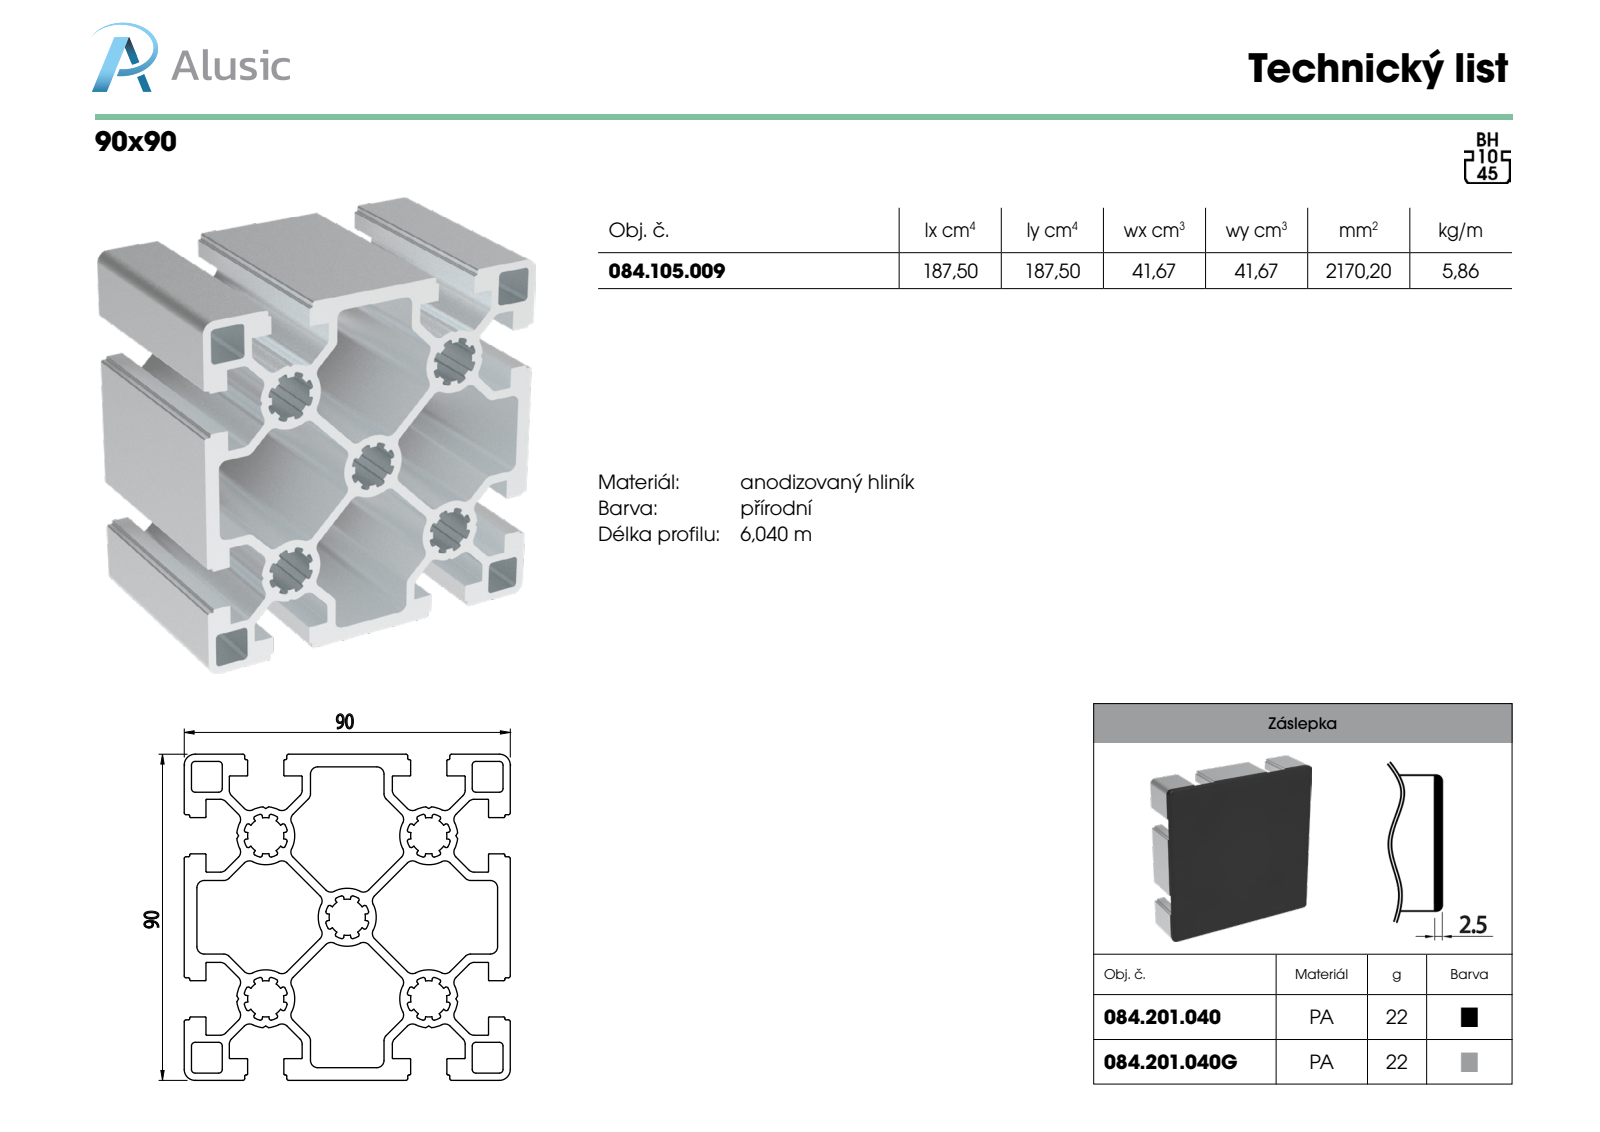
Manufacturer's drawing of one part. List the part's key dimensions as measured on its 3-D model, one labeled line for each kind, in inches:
Part name (STEP PRODUCT): 084.105.009
STEP written by: SolidWorks 2018 (AUTOMOTIVE_DESIGN)
Units: inches
Bodies: 1 solid, 648 faces (250 planar, 398 cylindrical, 0 other)
Overall size (bounding box): 3.937 × 3.543 × 3.543
Volume: 13.24 in³ · Surface area: 244.4 in²
Partial cylindrical surfaces — rounded edges, fillets, slot ends (radius × count): R0.02 ×96, R0.079 ×72, R0.008 ×32, R0.012 ×32, R0.039 ×16, R0.197 ×5, R0.24 ×5, R0.315 ×5
Main face-to-face distances: 0.091, 3.543, 0.276, 0.236, 3.307, 0.138, 3.406, 0.098, 3.169, 1.772
